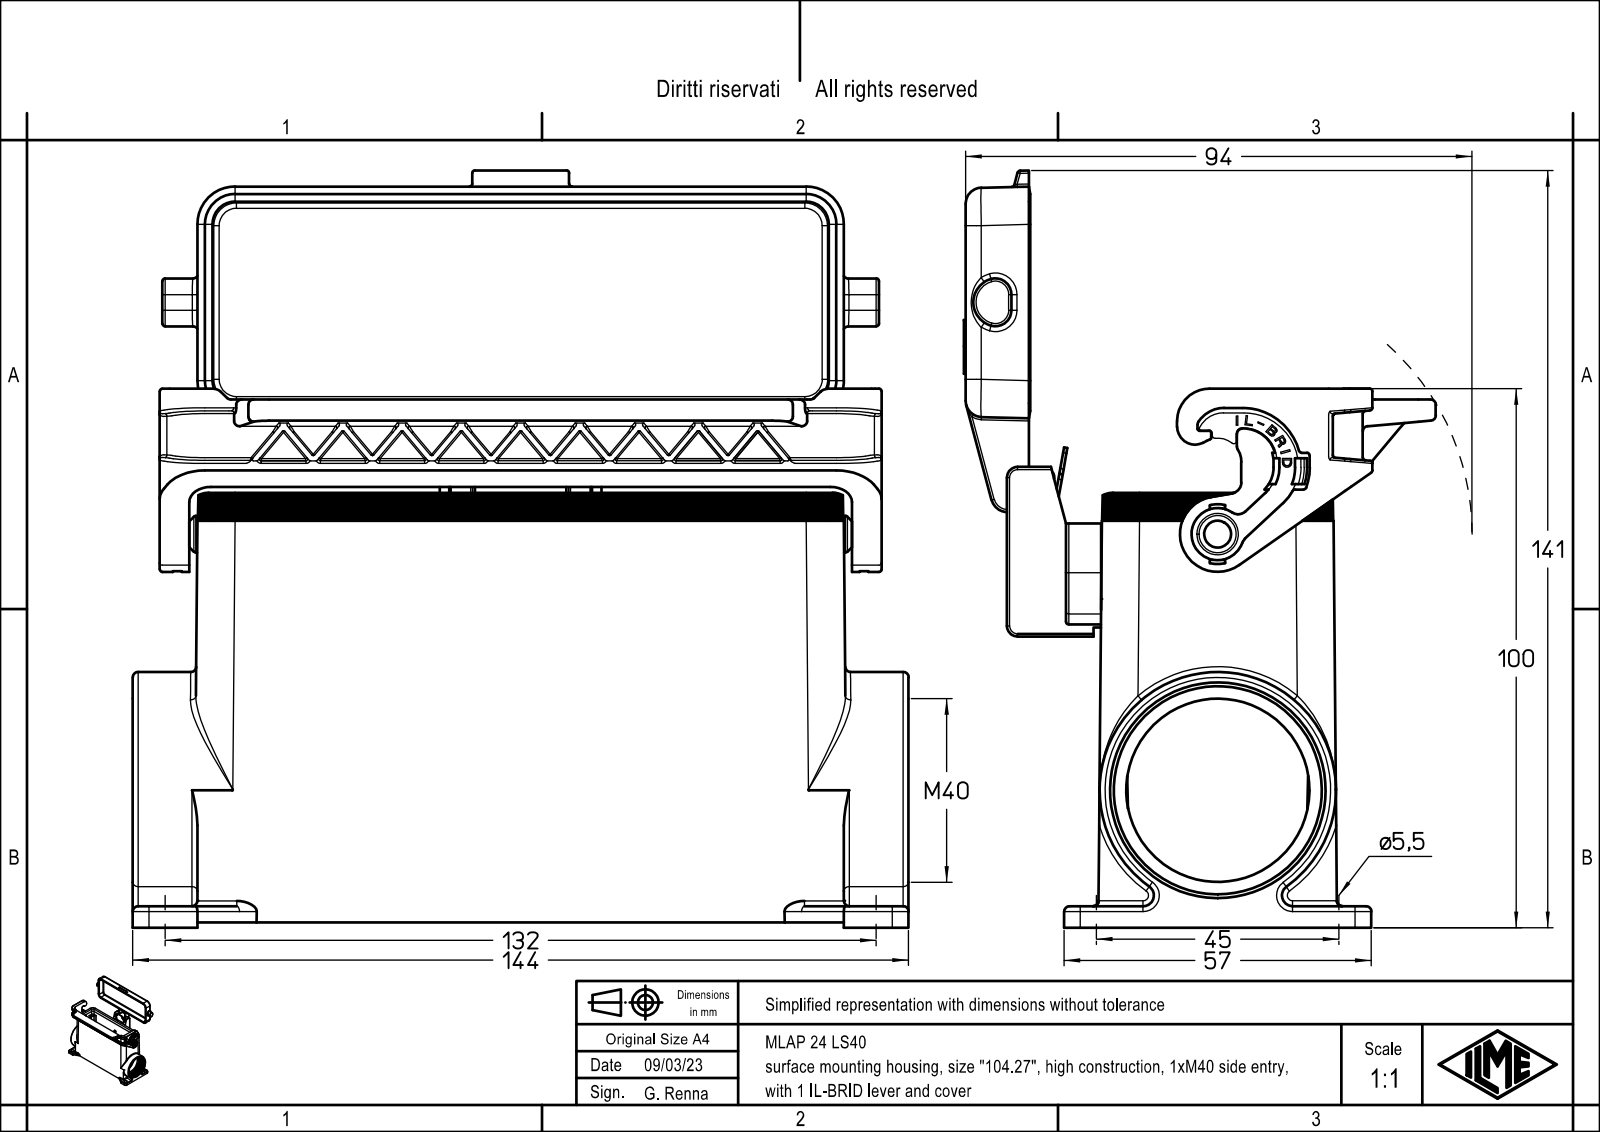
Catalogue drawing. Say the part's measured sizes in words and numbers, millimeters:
The part is named "MLAP 24 LS40". Its 3-D file was written by "Creo Elements/Direct Modeling 20.1B 02-Apr-2019 (C) Parametric Technology GmbH (AUTOMOTIVE_DESIGN)". It is 1 solid with 1408 faces: 835 planar, 404 cylindrical and 169 other. Overall it measures 144 by 140.49 by 87.76 millimeters. Its volume is 187 952 cubic millimeters and its surface area 105 051 square millimeters. Round holes: 4 of diameter 3, 4 of diameter 3.5, 4 of diameter 5.5, 1 of diameter 3.25, 1 of diameter 5.4, 1 of diameter 7.7, 1 of diameter 34, 1 of diameter 38.6. Round bosses or shafts: 1 of diameter 43.87, 1 of diameter 8.4, 1 of diameter 6.9, 1 of diameter 6.8, 1 of diameter 5.2, 1 of diameter 3.2. Partial cylindrical surfaces (rounded edges, fillets, slot ends): 29 of radius 0.5, 27 of radius 0.1, 24 of radius 1, 23 of radius 0.2, 23 of radius 3, 17 of radius 0.17, 16 of radius 0.33, 15 of radius 2. The main face-to-face distances are 2, 3, 2.8, 69.71, 71.71, 5.5, 7, 4, 97, 94. The hole center spacings are 16.64, 38.63, 118.34, 123.37, 27, 45, 104, 107.45.
